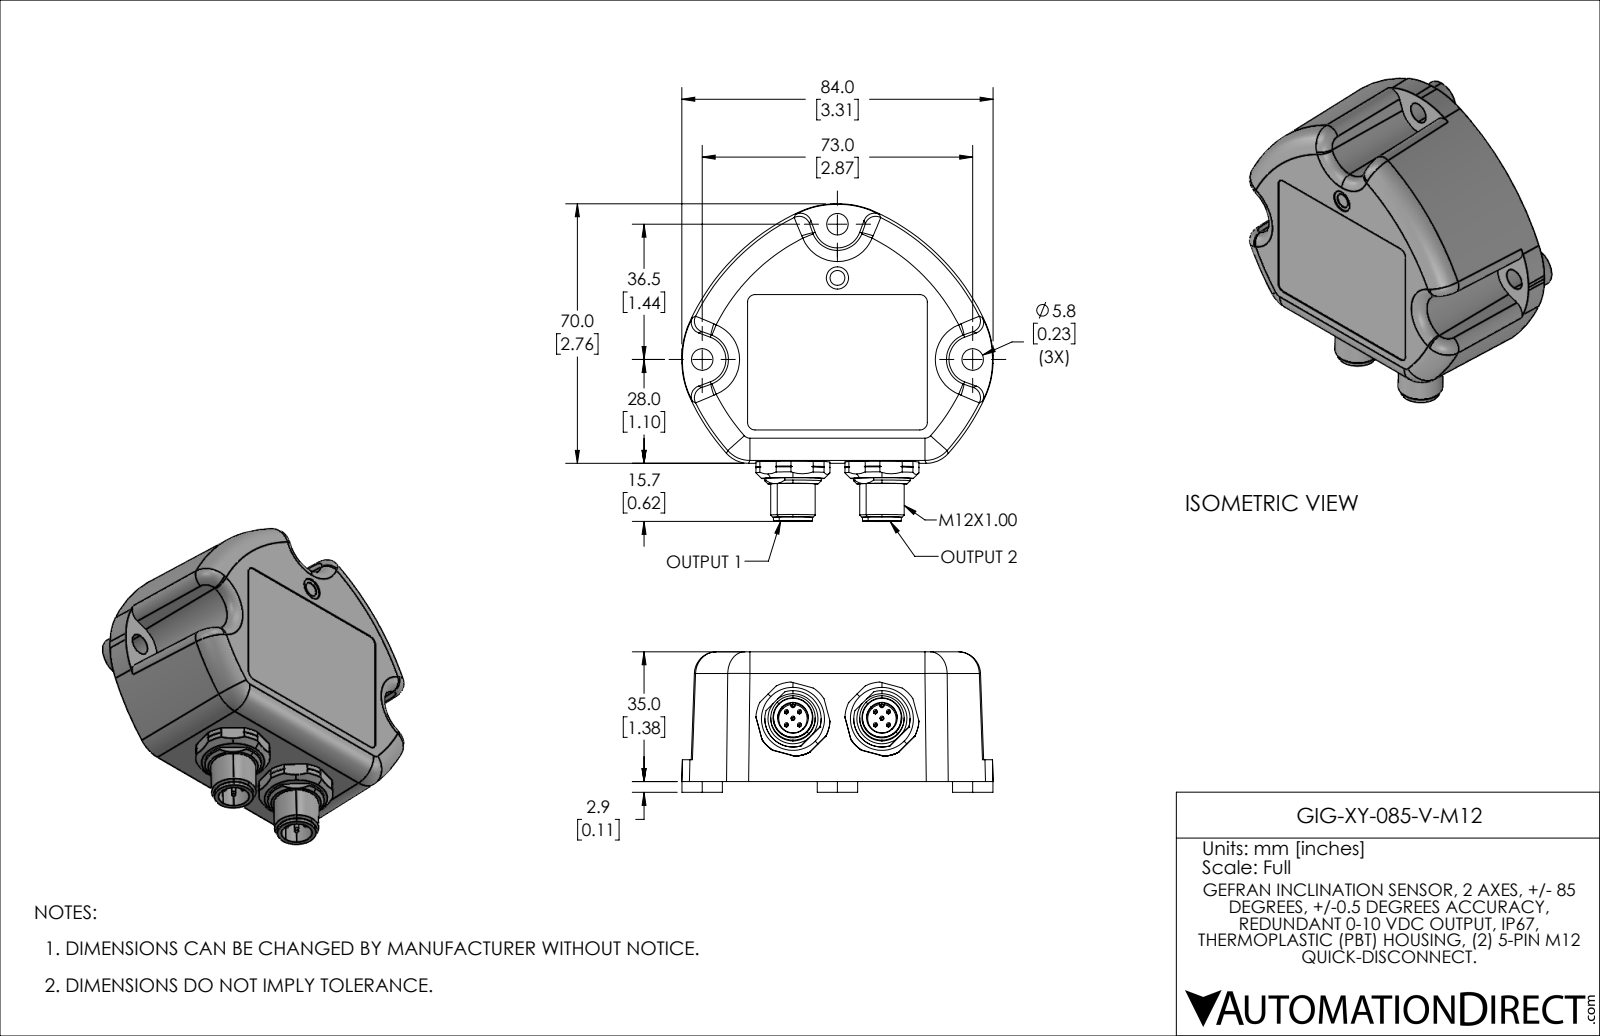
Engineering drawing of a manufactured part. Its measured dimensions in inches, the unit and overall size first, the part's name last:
Units: inches
Overall size (bounding box): 3.374 × 3.307 × 1.492
Round holes (diameter × count): ⌀0.228 ×3, ⌀0.327 ×2, ⌀0.157 ×1, ⌀0.236 ×1
Round bosses / shafts (diameter × count): ⌀0.039 ×10, ⌀0.429 ×3, ⌀0.472 ×2, ⌀0.413 ×2
Partial cylindrical surfaces — rounded edges, fillets, slot ends (radius × count): R0.02 ×4, R0.079 ×4, R0.299 ×3, R0.024 ×2, R0.273 ×2, R0.394 ×2, R0.236 ×1, R0.301 ×1
Main face-to-face distances: 1.37, 1.378, 0.232, 1.138, 1.146, 0.114, 0.346, 1.484, 1.492, 0.668
Hole centre spacings: 1.678, 2.032, 0.571, 0.945, 2.874
Volume: 9.029 in³ · Surface area: 32.38 in²
Bodies: 1 solid, 365 faces (87 planar, 123 cylindrical, 155 other)
Part name (STEP PRODUCT): GIG-XY-085-V-M12
STEP written by: SolidWorks 2021 (AUTOMOTIVE_DESIGN)
